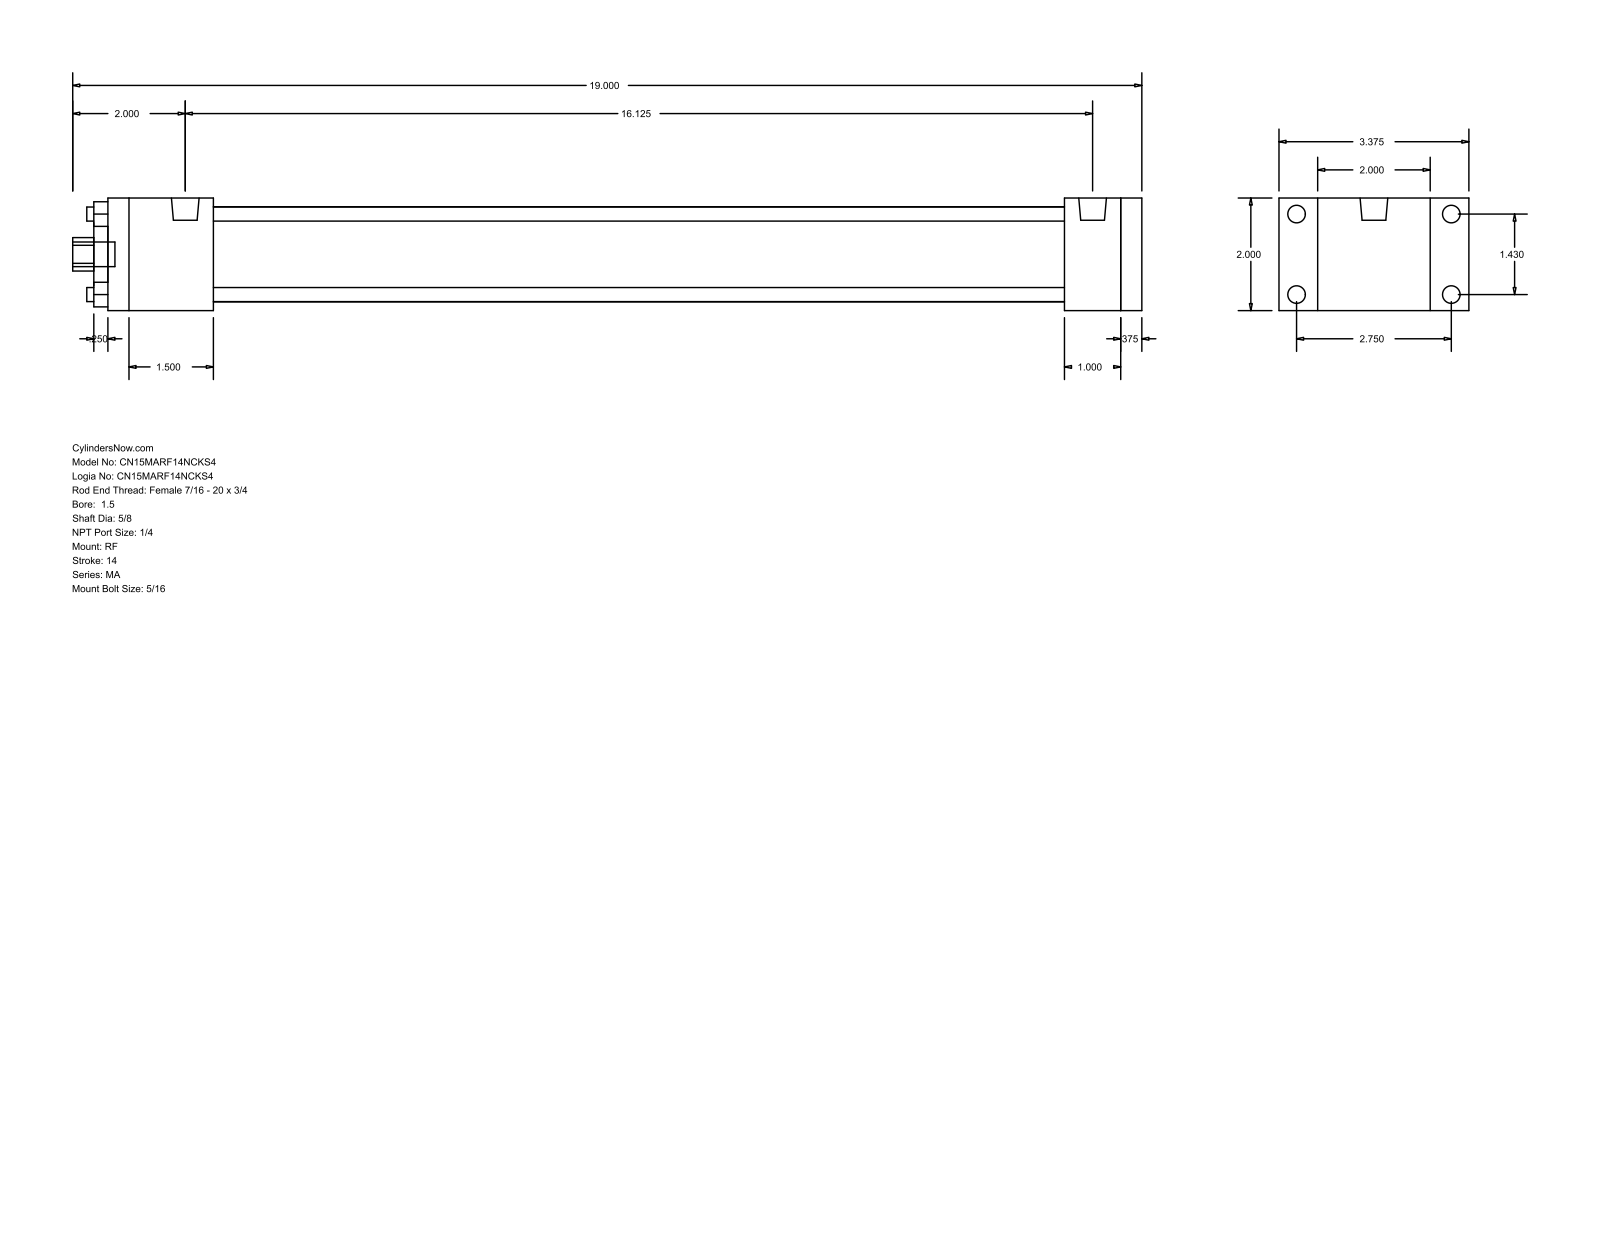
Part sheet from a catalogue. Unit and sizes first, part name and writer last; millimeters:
Units: millimetres
Overall size (bounding box): 482.6 × 85.72 × 50.8
Round holes (diameter × count): ⌀6.35 ×4, ⌀15.88 ×1, ⌀28.57 ×1, ⌀42.93 ×1
Round bosses / shafts (diameter × count): ⌀7.94 ×8, ⌀12.49 ×2, ⌀11.11 ×1
Partial cylindrical surfaces — rounded edges, fillets, slot ends (radius × count): R7.54 ×1
Main face-to-face distances: 50.8, 9.53, 466.72, 457.19, 431.8, 25.39, 34.92, 47.62, 384.18, 409.57
Hole centre spacings: 25.68, 36.32, 51.36
Bodies: 0 solids, 92 faces (64 planar, 28 cylindrical, 0 other)
Part name (STEP PRODUCT): MA_RF__0150_0.625
STEP written by: GSSL Pune (CONFIG_CONTROL_DESIGN)
